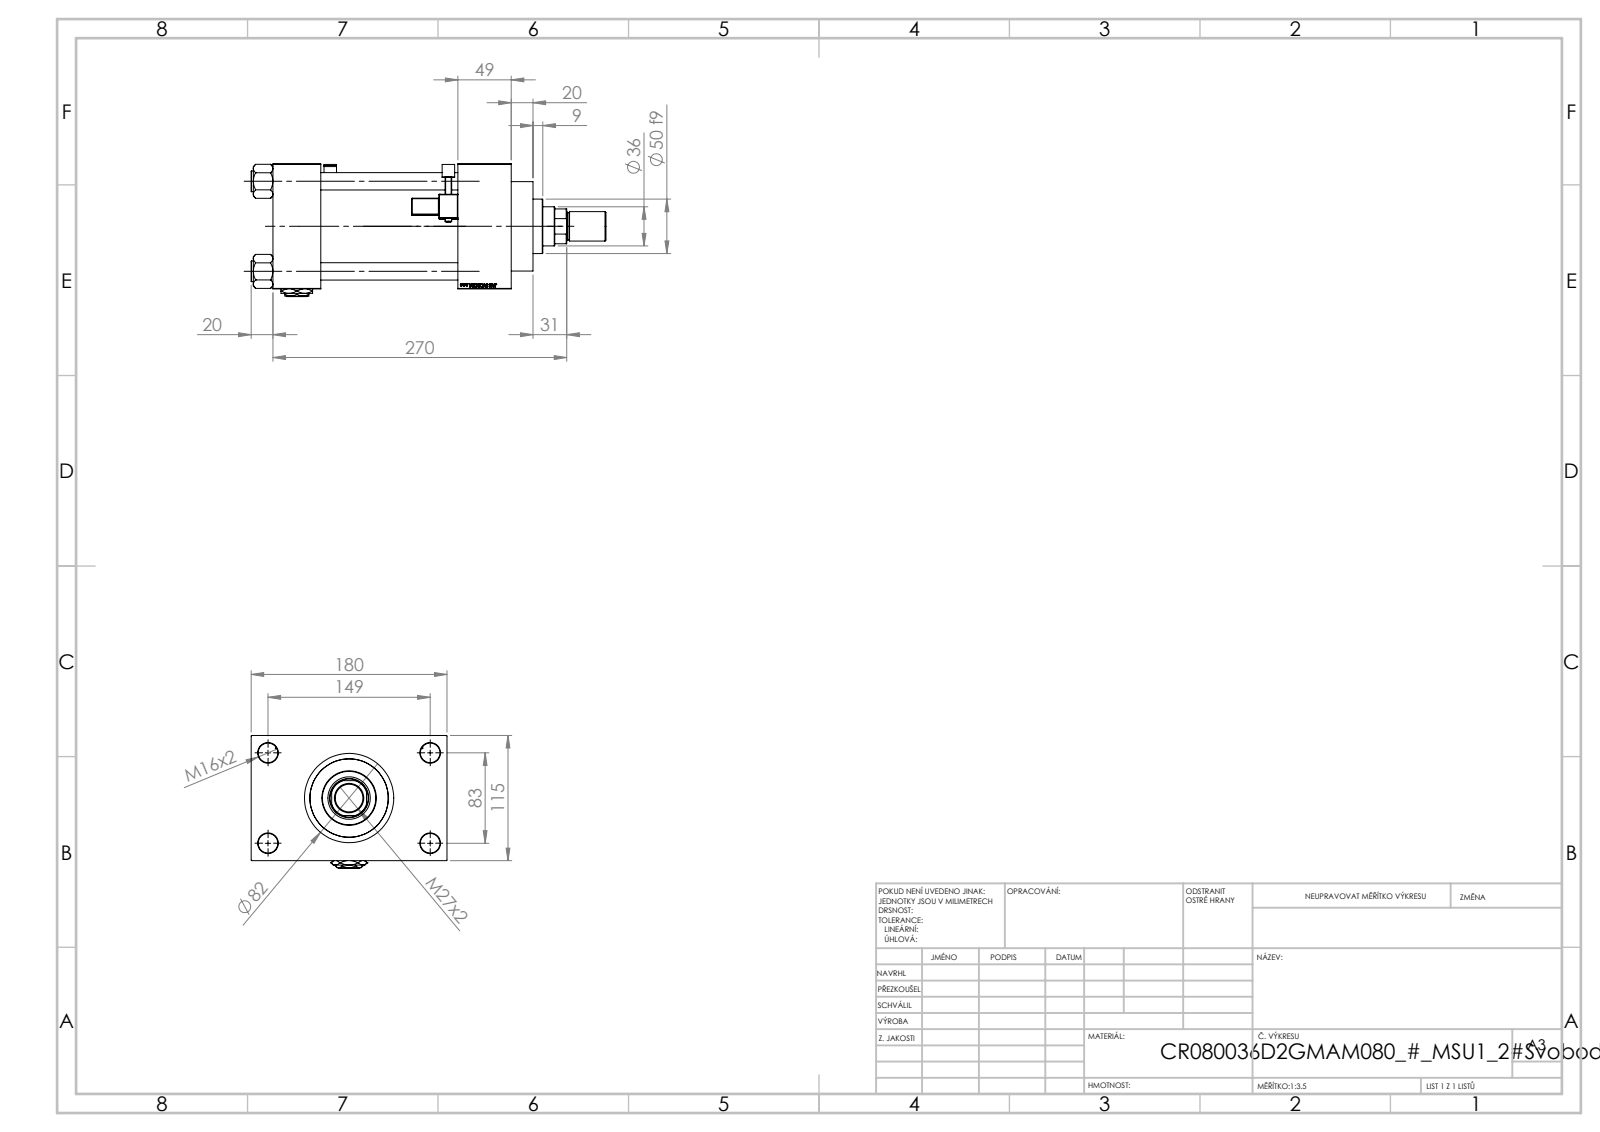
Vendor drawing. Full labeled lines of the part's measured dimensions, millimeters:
Part name (STEP PRODUCT): V215_VC_A; NUT_M5_D; V215CR_VCP_D; ROD_END_AH (+4 more)
STEP written by: SolidWorks 2019 (CONFIG_CONTROL_DESIGN)
Units: millimetres
Bodies: 15 solids, 1372 faces (631 planar, 159 cylindrical, 582 other)
Overall size (bounding box): 326 × 180 × 122
Volume: 2 194 000 mm³ · Surface area: 367 092 mm²
Round holes (diameter × count): ⌀16 ×4, ⌀18 ×4, ⌀7 ×3, ⌀26.44 ×3, ⌀35 ×3, ⌀25.5 ×1, ⌀36 ×1, ⌀39 ×1, ⌀61 ×1, ⌀72 ×1, ⌀80 ×1
Round bosses / shafts (diameter × count): ⌀19 ×4, ⌀6 ×2, ⌀86 ×1, ⌀82 ×1, ⌀50 ×1, ⌀27 ×1, ⌀25 ×1
Partial cylindrical surfaces — rounded edges, fillets, slot ends (radius × count): R0.5 ×48, R1 ×2, R2.5 ×2, R4 ×2, R17.5 ×1
Main face-to-face distances: 115, 126, 175, 49, 170, 44, 219, 32.5, 147.5, 180
Hole centre spacings: 33.15, 58.48, 82.7, 85.28, 89.24, 115.85, 142.43, 83
